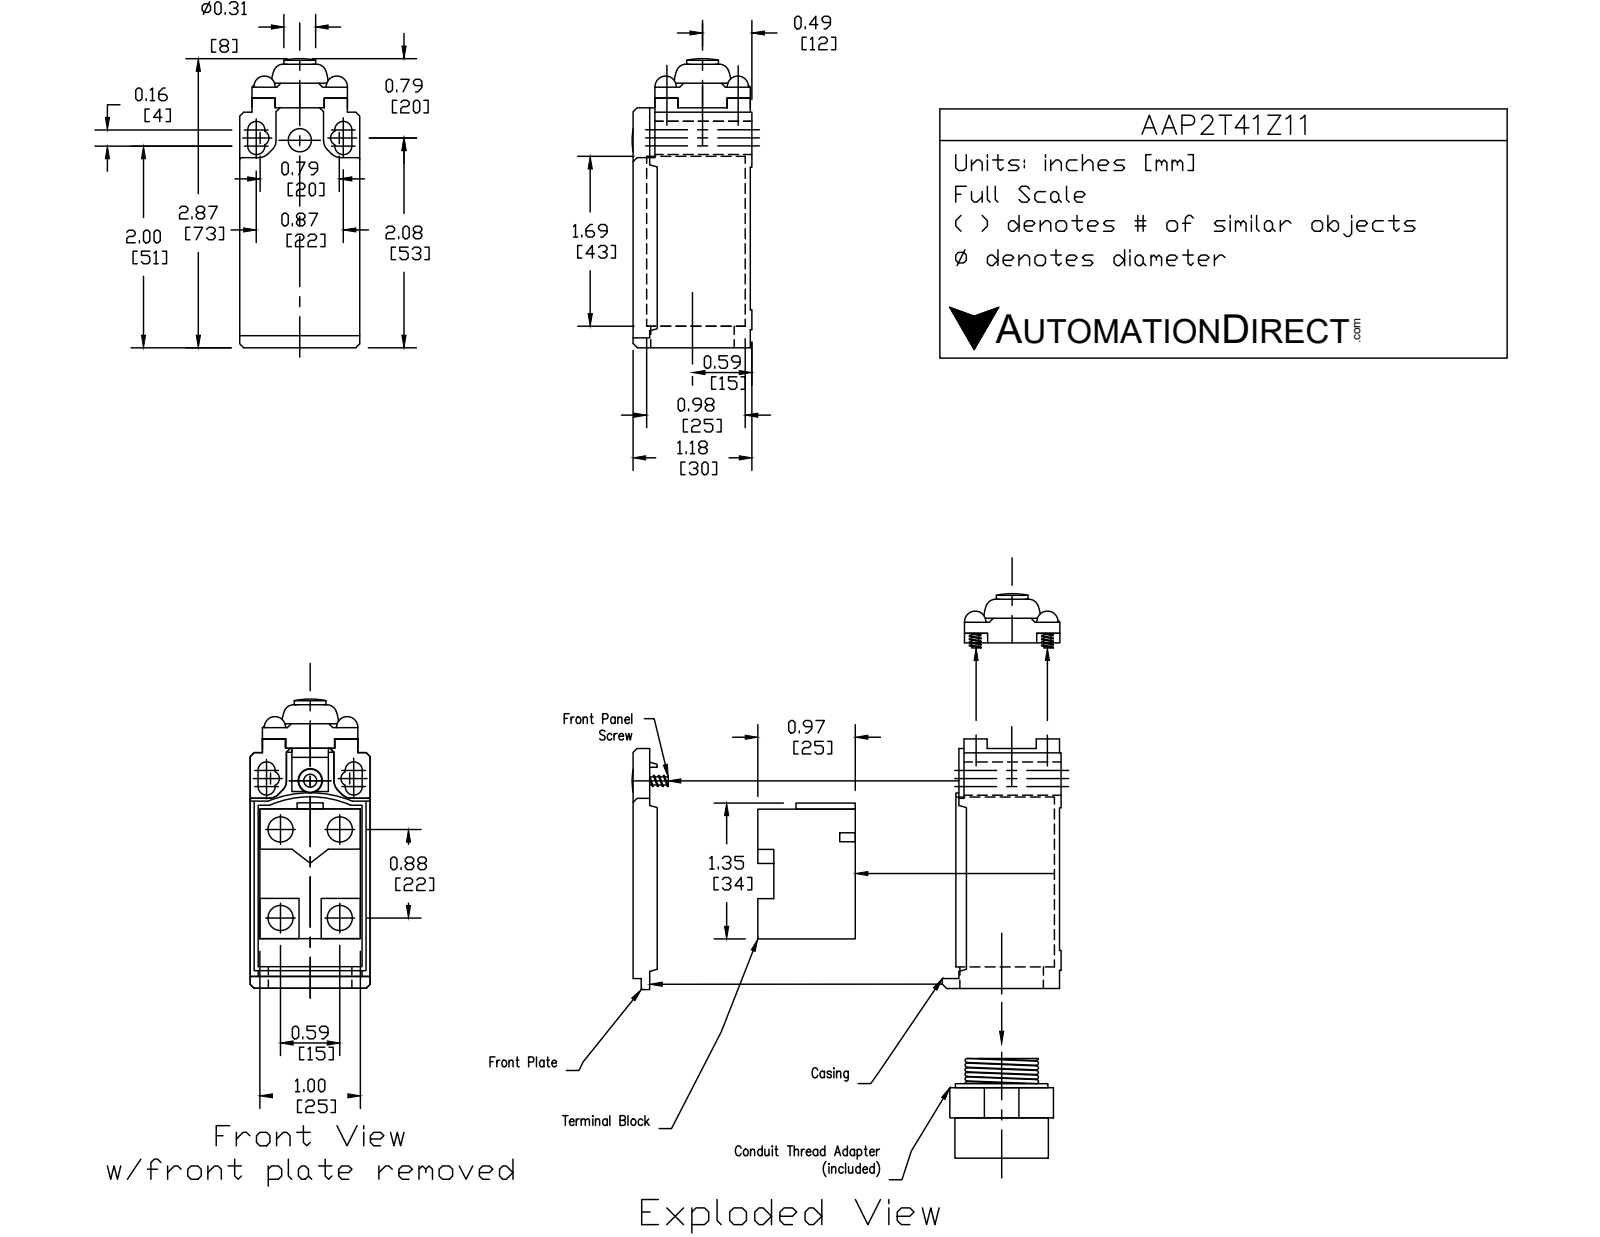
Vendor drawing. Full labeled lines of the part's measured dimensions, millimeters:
Part name (STEP PRODUCT): AAP2T14Z11
STEP written by: SolidWorks 2017 (AUTOMOTIVE_DESIGN)
Units: millimetres
Bodies: 4 solids, 184 faces (104 planar, 60 cylindrical, 20 other)
Overall size (bounding box): 73.3 × 30.6 × 30.3
Volume: 55 060 mm³ · Surface area: 13 260 mm²
Round holes (diameter × count): ⌀6 ×1, ⌀8.1 ×1, ⌀14.5 ×1, ⌀17 ×1, ⌀19 ×1
Round bosses / shafts (diameter × count): ⌀5.6 ×5, ⌀14.3 ×1, ⌀8 ×1, ⌀6.5 ×1
Partial cylindrical surfaces — rounded edges, fillets, slot ends (radius × count): R1 ×8, R3 ×8, R2 ×6, R10 ×1, R10.2 ×1
Main face-to-face distances: 30.3, 29.6, 0.4, 61.1, 6, 30, 24, 1.1, 66.2, 6.2
Hole centre spacings: 2.1
